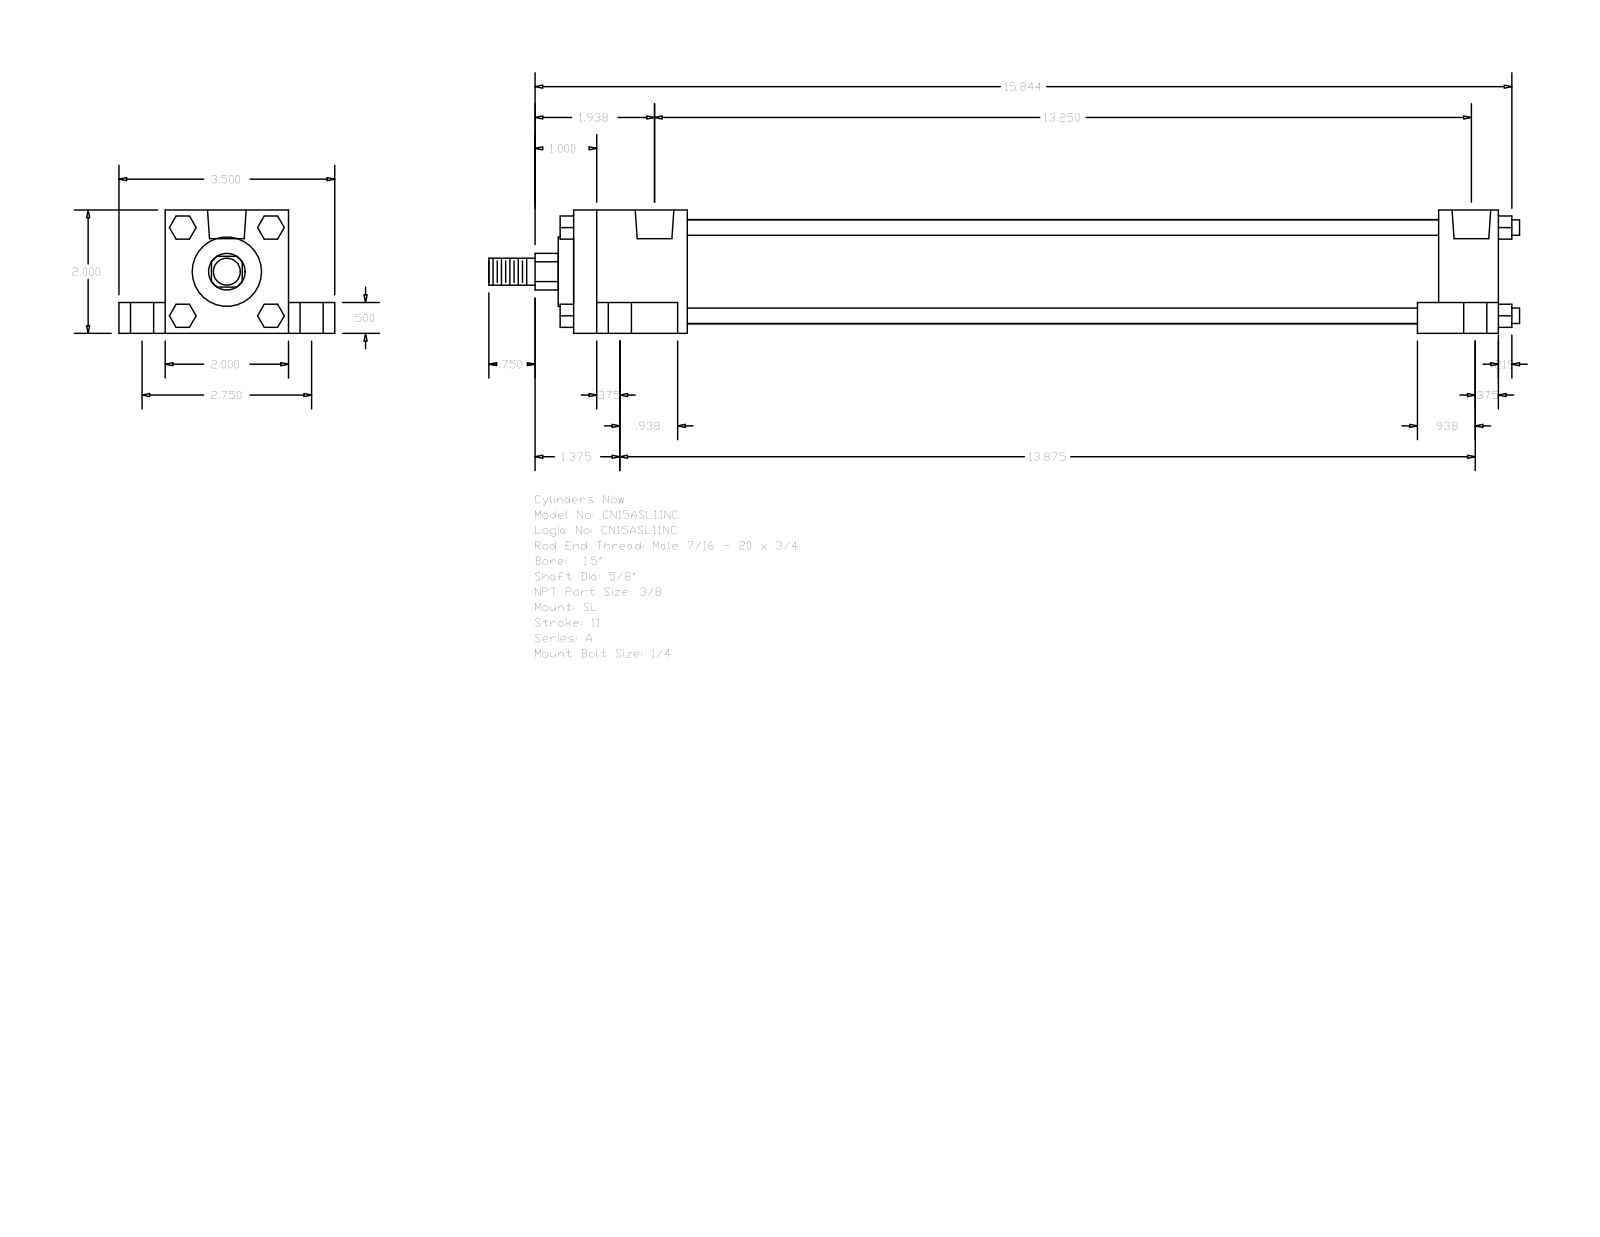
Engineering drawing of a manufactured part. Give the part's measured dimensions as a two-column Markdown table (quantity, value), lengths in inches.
| quantity | value |
| --- | --- |
| part name | A_SL__0150_0.625 |
| STEP written by | GSSL Pune (CONFIG_CONTROL_DESIGN) |
| units | inches |
| bodies | 0 solids, 148 faces (112 planar, 36 cylindrical, 0 other) |
| overall size | 16.719 × 3.5 × 2 |
| round holes (diameter × count) | 0.219 × 4, 0.375 × 4, 0.625 × 4, 0.627 × 2 |
| round bosses / shafts (diameter × count) | 0.25 × 4, 1.69 × 1, 1.125 × 1, 0.625 × 1, 0.437 × 1 |
| partial cylindrical surfaces (radius × count) | 0.297 × 1 |
| main face-to-face distances | 2, 0.75, 1.5, 0.5, 2.75, 15, 0.375, 1.313, 14.031, 0.969 |
| hole center spacings | 0.156, 1.376, 1.392, 1.485, 1.552, 2.75, 12.937, 13.094 |
